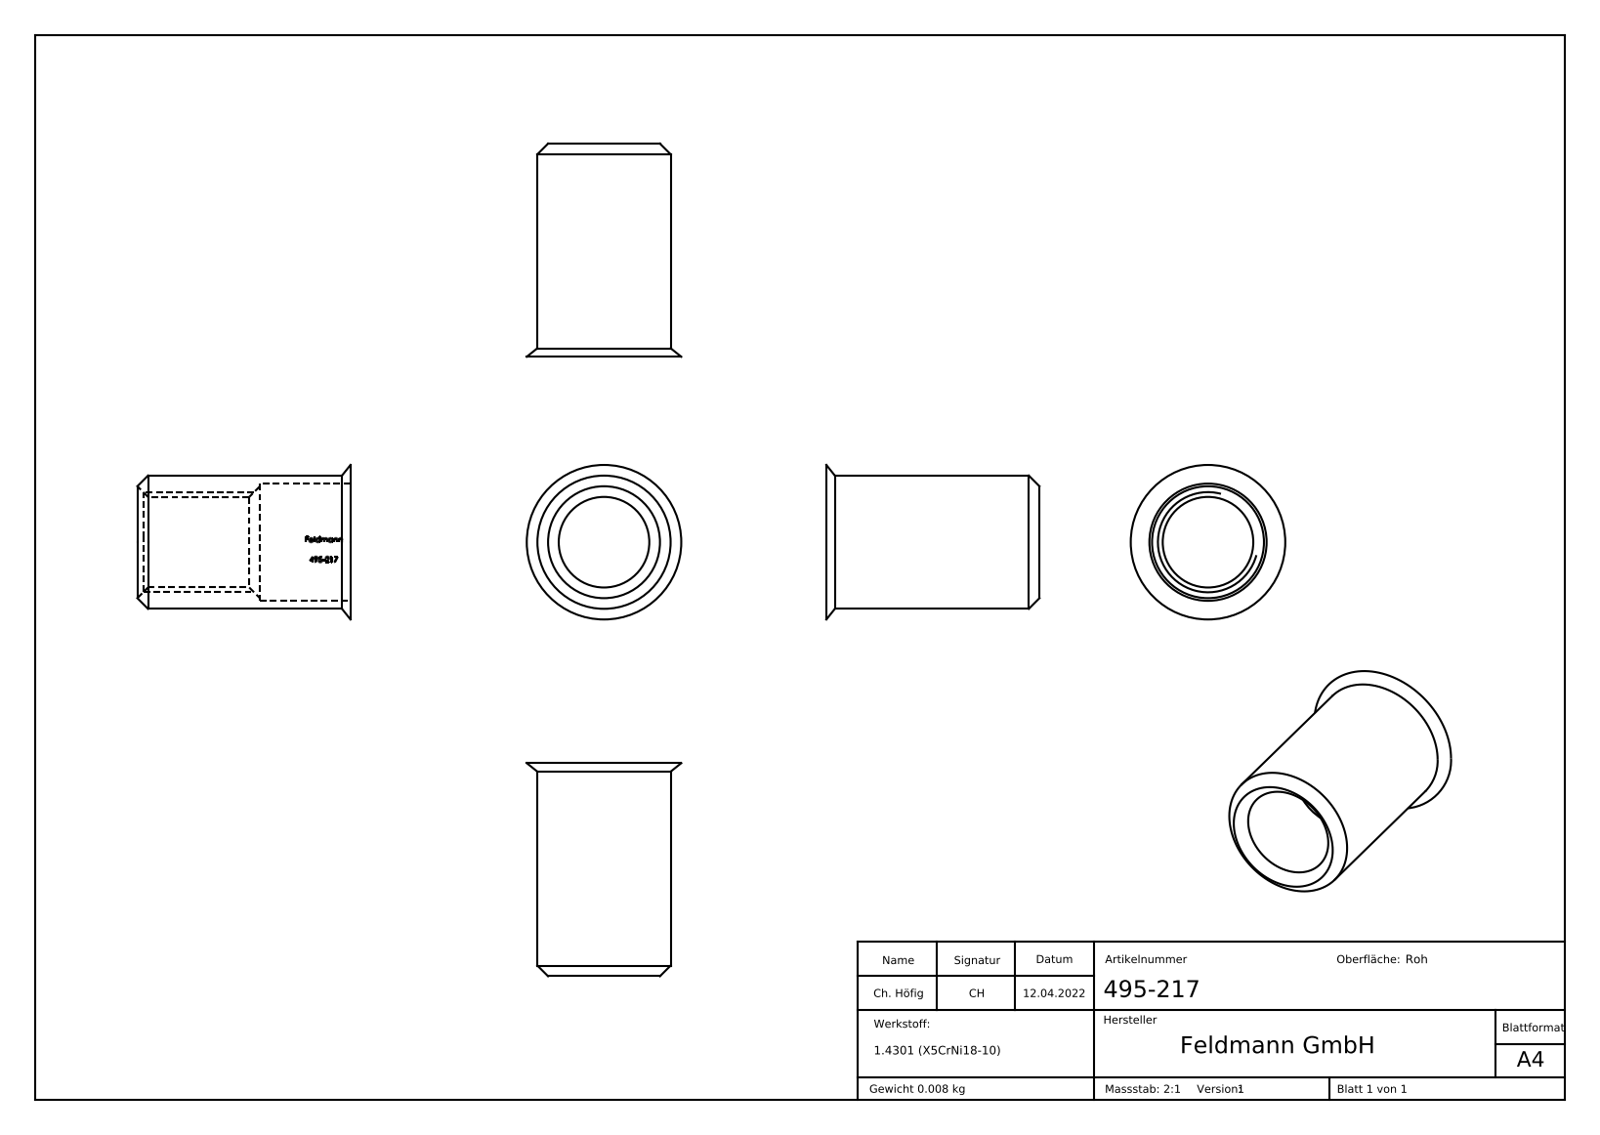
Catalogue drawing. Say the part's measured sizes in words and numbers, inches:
The part is named "495-217". Its 3-D file was written by "SolidWorks 2018 (CONFIG_CONTROL_DESIGN)". It is 1 solid with 210 faces: 100 planar, 29 cylindrical and 81 other. Overall it measures 0.787 by 0.571 by 0.571 inches. Its volume is 0.059 cubic inches and its surface area 2.378 square inches. Round holes: 1 of diameter 0.335, 1 of diameter 0.433. Round bosses or shafts: 1 of diameter 0.492. Partial cylindrical surfaces (rounded edges, fillets, slot ends): 1 of radius 0.22. The main face-to-face distances are 0.335, 0.072, 0.026, 0.053, 0.074, 0.047, 0.066, 0.069, 0.064, 0.07.
